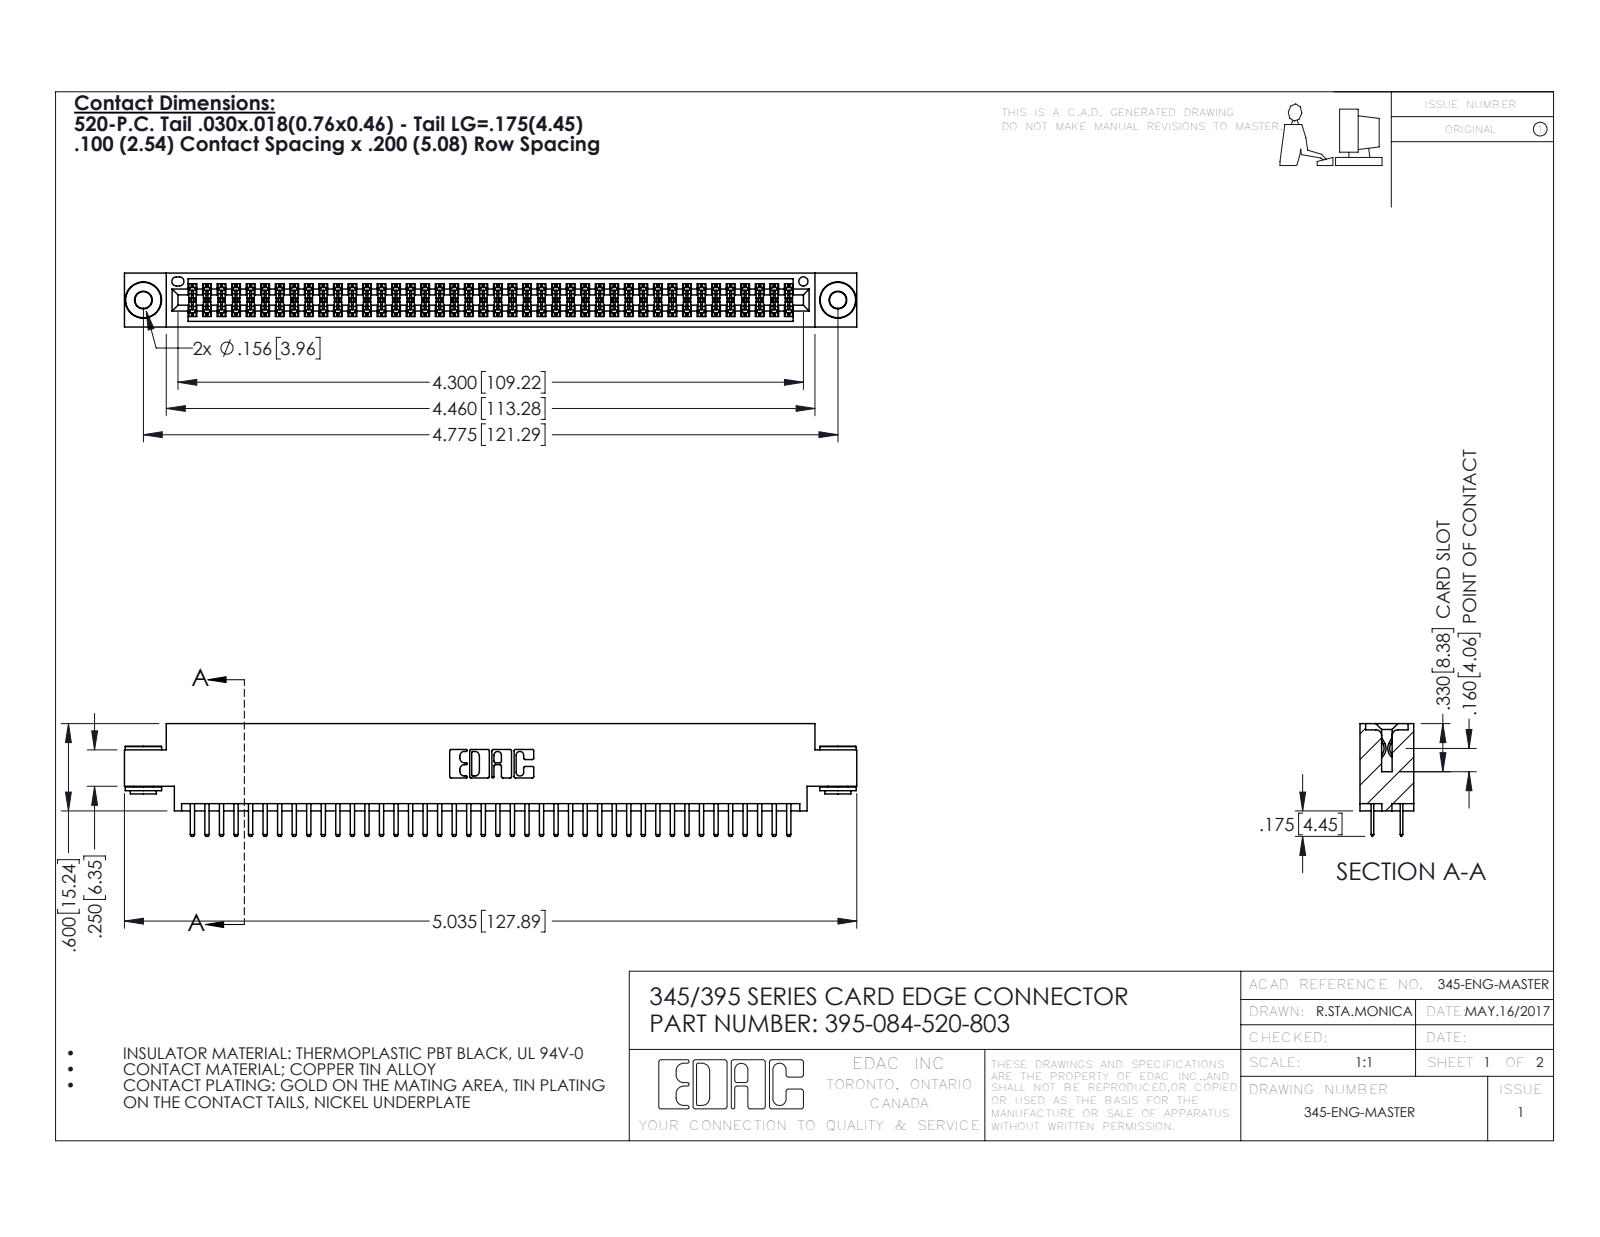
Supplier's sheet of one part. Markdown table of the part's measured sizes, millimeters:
| quantity | value |
| --- | --- |
| part name | 345-250-002_345-250-002-102; 395-084-520-803; 345-292-001_345-293-120; 345 Part_0.170 Offset - 0.156 Dia-TH |
| STEP written by | SolidWorks 2016 (CONFIG_CONTROL_DESIGN) |
| units | millimeters |
| bodies | 87 solids, 4704 faces (3034 planar, 1662 cylindrical, 8 other) |
| overall size | 127.9 × 19.7 × 9.4 |
| volume | 12 300 mm³ |
| surface area | 18 440 mm² |
| round holes (diameter × count) | 2.9 × 2, 4 × 2, 1.6 × 1 |
| round bosses / shafts (diameter × count) | 6.4 × 2, 4.6 × 2, 3.5 × 2 |
| partial cylindrical surfaces (radius × count) | 0.2 × 126, 0.3 × 88, 0.3 × 22, 0.2 × 6, 0.8 × 6, 0.7 × 3, 0.4 × 2, 0.5 × 2 |
| main face-to-face distances | 1.8, 7.6, 5.1, 9.4, 2.5, 6.9, 0.6, 5.7, 4.4, 0.6 |
| hole center spacings | 6.9, 115.3, 121.3 |
